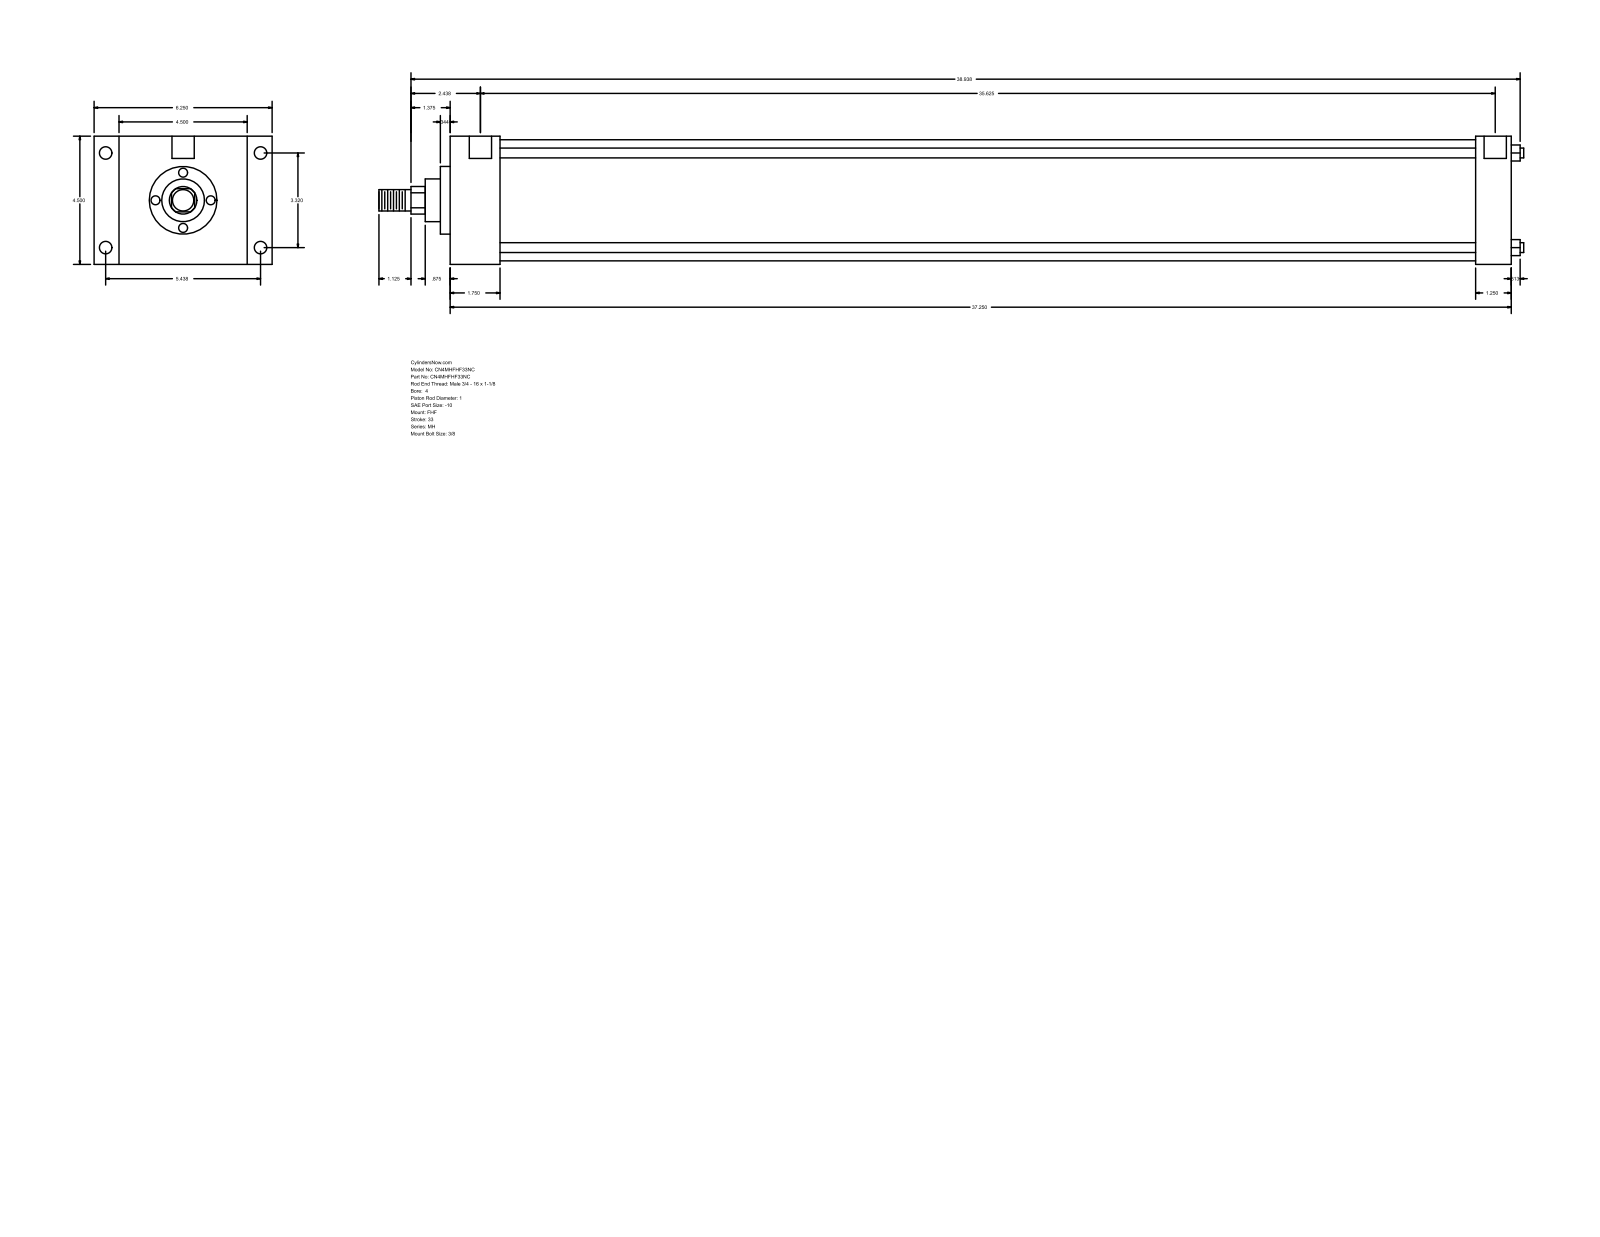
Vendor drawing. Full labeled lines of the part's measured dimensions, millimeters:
Part name (STEP PRODUCT): MH_FHF__0400_1
STEP written by: GSSL Pune (CONFIG_CONTROL_DESIGN)
Units: millimetres
Bodies: 0 solids, 90 faces (61 planar, 29 cylindrical, 0 other)
Overall size (bounding box): 1020.76 × 158.75 × 114.3
Round holes (diameter × count): ⌀8.73 ×4, ⌀11.13 ×4, ⌀19.84 ×2
Round bosses / shafts (diameter × count): ⌀8.76 ×4, ⌀107.95 ×1, ⌀60.33 ×1, ⌀38.1 ×1, ⌀25.4 ×1, ⌀19.05 ×1
Partial cylindrical surfaces — rounded edges, fillets, slot ends (radius × count): R12.29 ×1
Main face-to-face distances: 114.3, 946.16, 44.46, 901.7, 22.23, 136.53, 158.76, 914.41, 869.95, 31.75
Hole centre spacings: 84.32, 138.12, 161.82, 908.05, 1.58, 1.59, 904.88, 906.46
